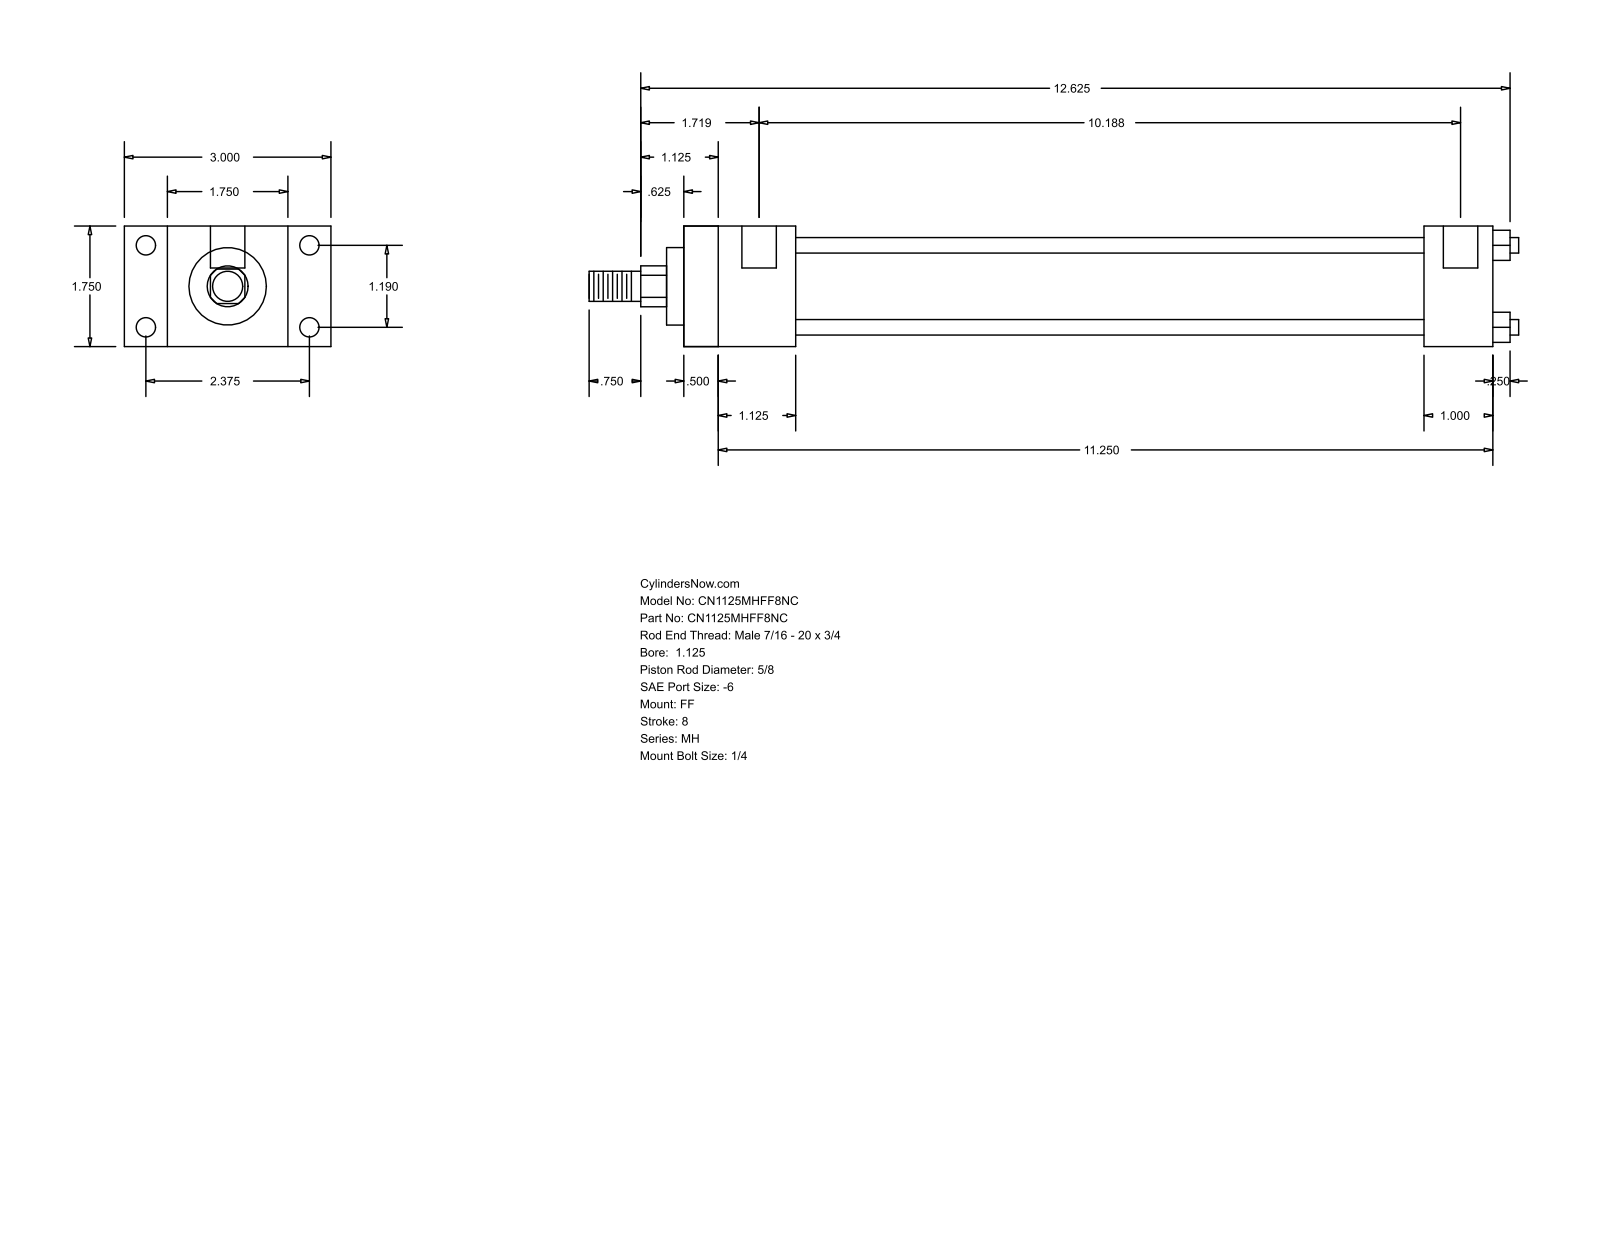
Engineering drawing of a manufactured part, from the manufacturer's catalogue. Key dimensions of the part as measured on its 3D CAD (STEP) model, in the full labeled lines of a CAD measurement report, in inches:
Part name (STEP PRODUCT): MH_FF__0112_0.625
STEP written by: GSSL Pune (CONFIG_CONTROL_DESIGN)
Units: inches
Bodies: 0 solids, 92 faces (64 planar, 28 cylindrical, 0 other)
Overall size (bounding box): 13.5 × 3 × 1.75
Round holes (diameter × count): ⌀0.219 ×4, ⌀0.281 ×4, ⌀0.5 ×2
Round bosses / shafts (diameter × count): ⌀0.225 ×4, ⌀1.375 ×1, ⌀1.125 ×1, ⌀0.625 ×1, ⌀0.437 ×1
Partial cylindrical surfaces — rounded edges, fillets, slot ends (radius × count): R0.297 ×1
Main face-to-face distances: 1.75, 11.75, 0.625, 0.5, 11.25, 1.125, 2.375, 1.625, 10.75, 10.25
Hole centre spacings: 1.19, 2.375, 2.656, 10.063, 0.125, 10.187
